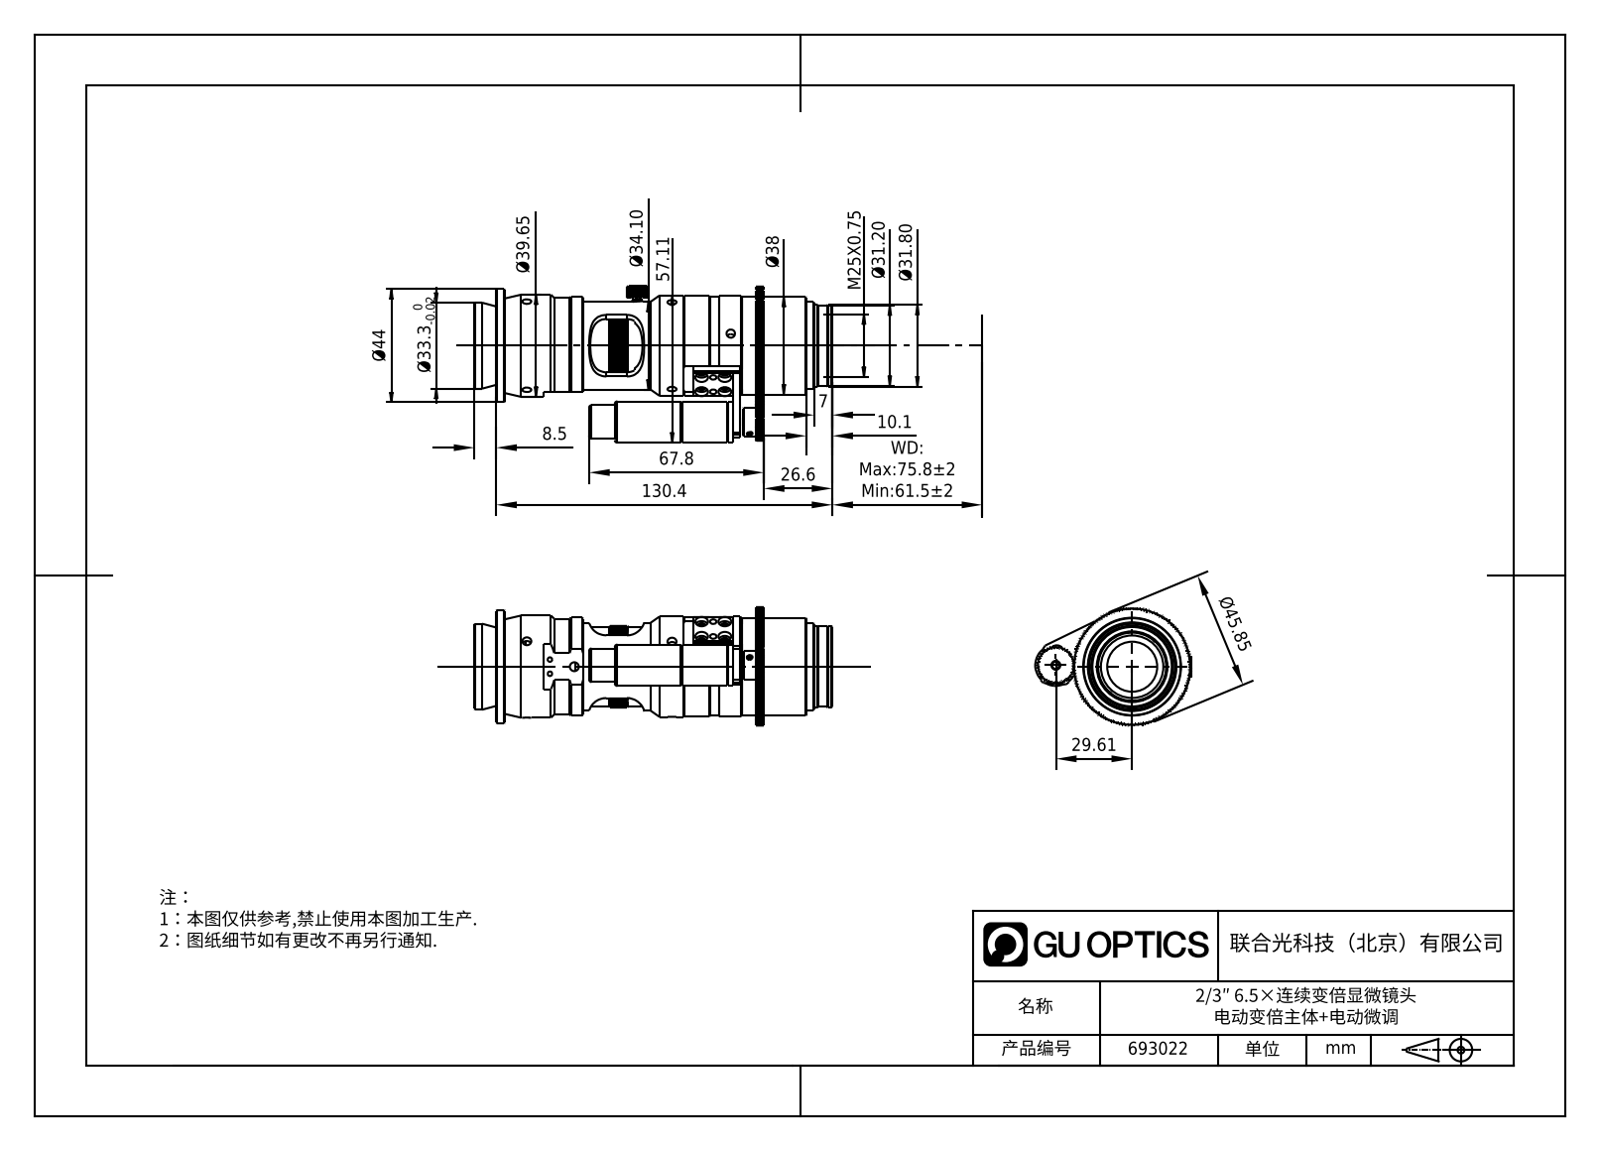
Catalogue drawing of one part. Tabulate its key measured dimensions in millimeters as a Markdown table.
| quantity | value |
| --- | --- |
| part name | VP-LZ-65110-12 |
| STEP written by | SolidWorks 2015 (CONFIG_CONTROL_DESIGN) |
| units | millimeters |
| bodies | 0 solids, 1053 faces (67 planar, 849 cylindrical, 137 other) |
| overall size | 139.7 × 64.59 × 60.52 |
| round holes (diameter × count) | 3.3 × 12, 5 × 8, 3 × 6, 2.05 × 5, 2.5 × 4, 5.5 × 3, 2.4 × 2, 31.2 × 1, 31.8 × 1, 33.3 × 1, 33.8 × 1, 38 × 1 |
| round bosses / shafts (diameter × count) | 16 × 2, 1.6 × 2, 1.1 × 2, 40.6 × 1, 39.6 × 1, 38.6 × 1, 38.1 × 1, 34 × 1 |
| partial cylindrical surfaces (radius × count) | 9.03 × 255, 2.8 × 73, 0.3 × 24, 5 × 2, 6.6 × 2, 6.56 × 1, 7.35 × 1, 20.5 × 1 |
| main face-to-face distances | 3, 8.5, 104.8, 51.4, 60.5, 34, 9.1, 42.5, 62.3, 96.3 |
| hole center spacings | 4.5, 9.18, 8, 10, 57.35, 7.99, 9, 12.04 |
